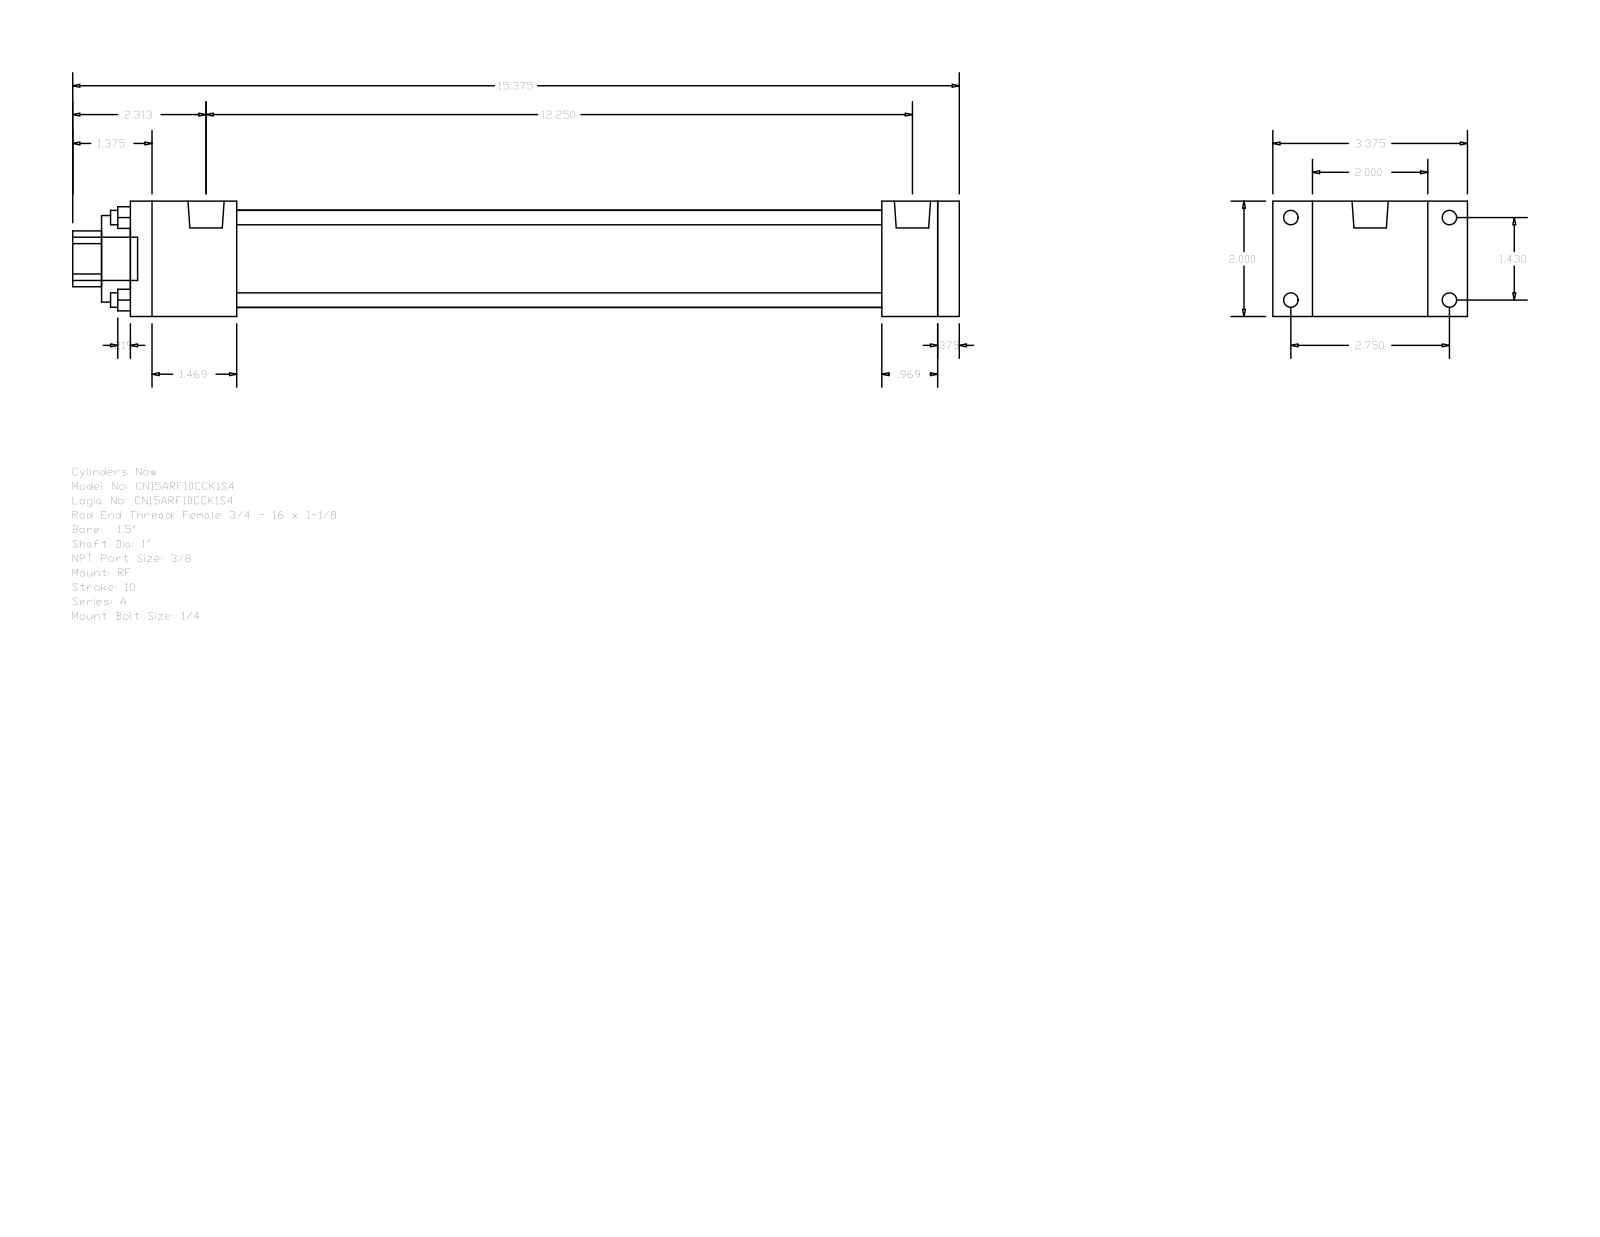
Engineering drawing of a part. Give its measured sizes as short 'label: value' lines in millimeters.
name: A_RF__0150_1
written by: GSSL Pune (CONFIG_CONTROL_DESIGN)
unit: mm
bodies: 0 solids, 92 faces (64 planar, 28 cylindrical, 0 other)
size: 390.52 × 85.72 × 50.8
holes: 4× ⌀6.35, 1× ⌀25.4, 1× ⌀38.1, 1× ⌀42.93
bosses: 4× ⌀6.35, 4× ⌀5.56, 2× ⌀15.93, 1× ⌀19.05
rounds: 1× R12.29
face distances: 50.8, 9.52, 355.6, 365.12, 330.99, 24.61, 34.13, 46.83, 284.16, 308.77
hole spacings: 25.68, 36.32, 51.36
